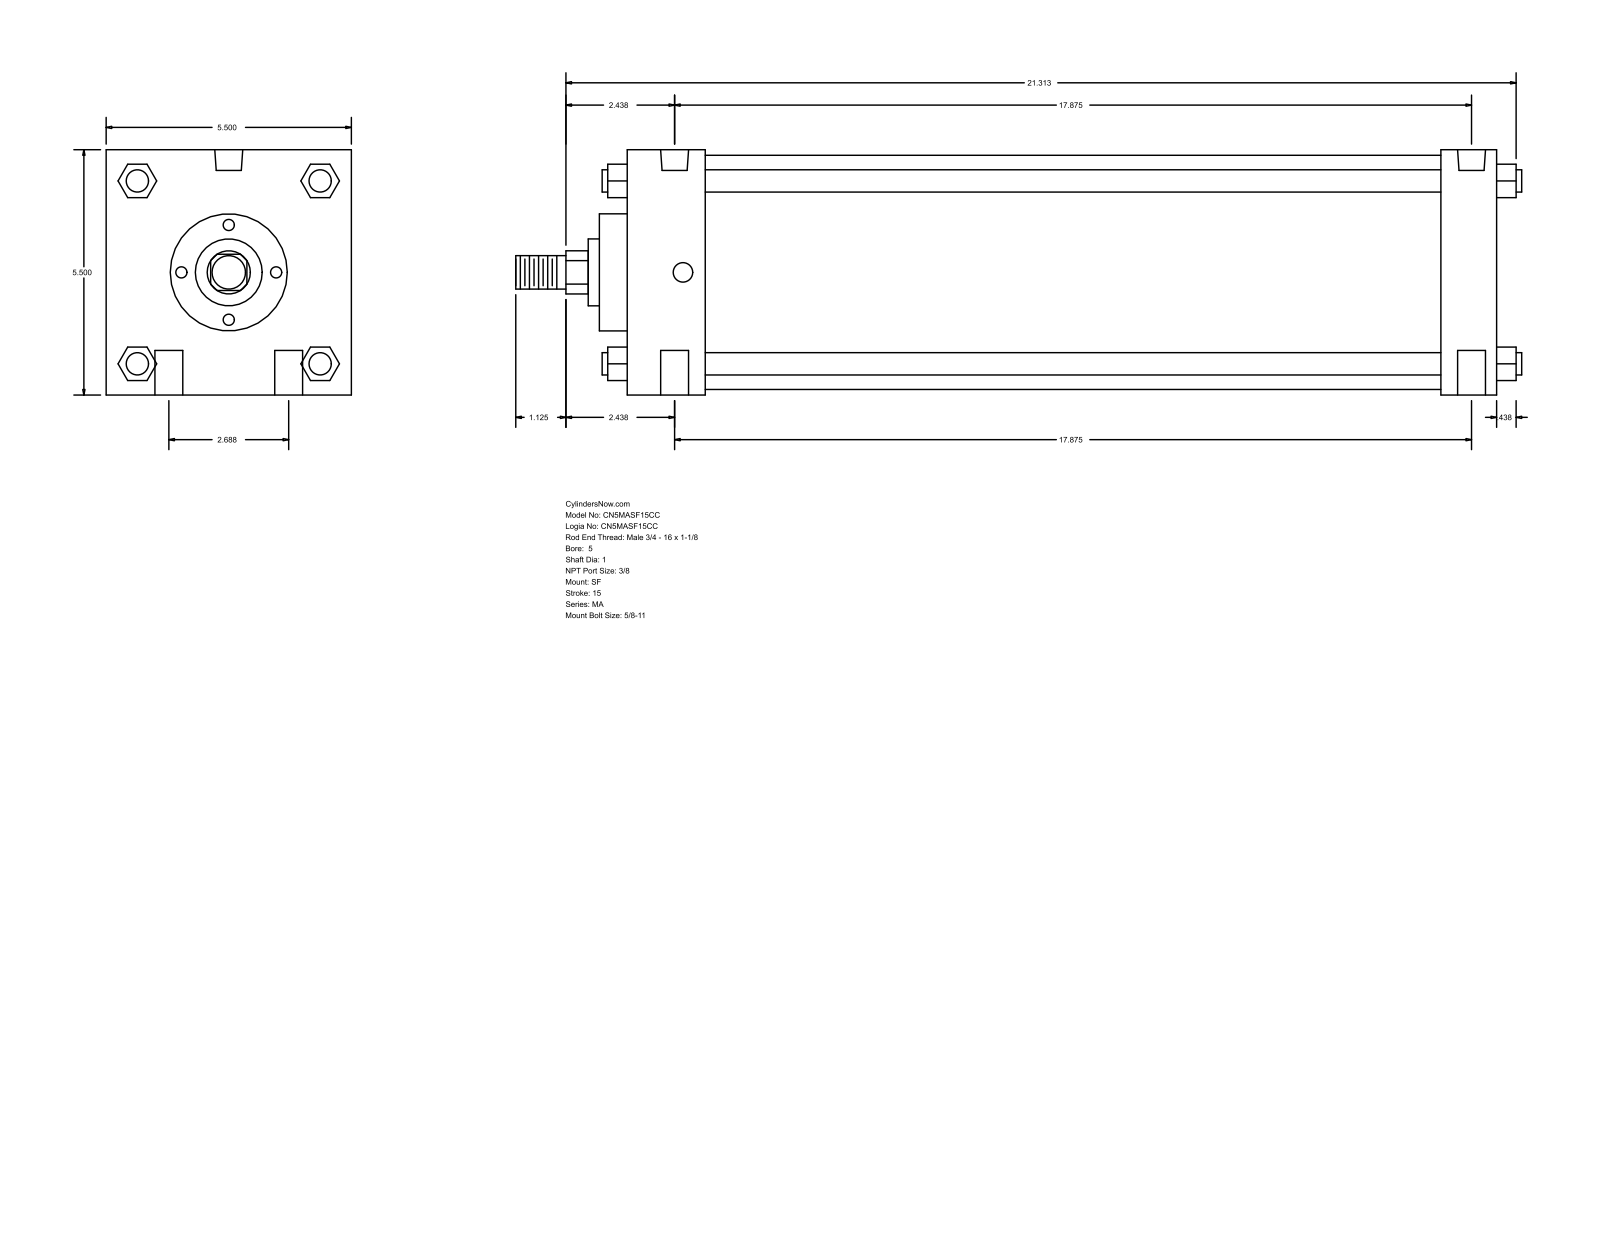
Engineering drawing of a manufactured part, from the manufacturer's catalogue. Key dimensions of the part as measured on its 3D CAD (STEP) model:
Part name (STEP PRODUCT): MA_SF__0500_1
STEP written by: GSSL Pune (CONFIG_CONTROL_DESIGN)
Units: millimetres
Bodies: 0 solids, 126 faces (95 planar, 31 cylindrical, 0 other)
Overall size (bounding box): 573.09 × 139.7 × 139.7
Round holes (diameter × count): ⌀15.88 ×4, ⌀11.11 ×2, ⌀15.93 ×2
Round bosses / shafts (diameter × count): ⌀12.7 ×4, ⌀133.35 ×1, ⌀66.67 ×1, ⌀38.1 ×1, ⌀25.4 ×1, ⌀19.05 ×1
Partial cylindrical surfaces — rounded edges, fillets, slot ends (radius × count): R12.29 ×1
Main face-to-face distances: 139.7, 495.31, 44.46, 463.56, 419.1, 450.85, 31.75, 15.87, 60.33, 479.43
Hole centre spacings: 34.13, 455.31, 454.03, 68.26, 459.13, 444.51
